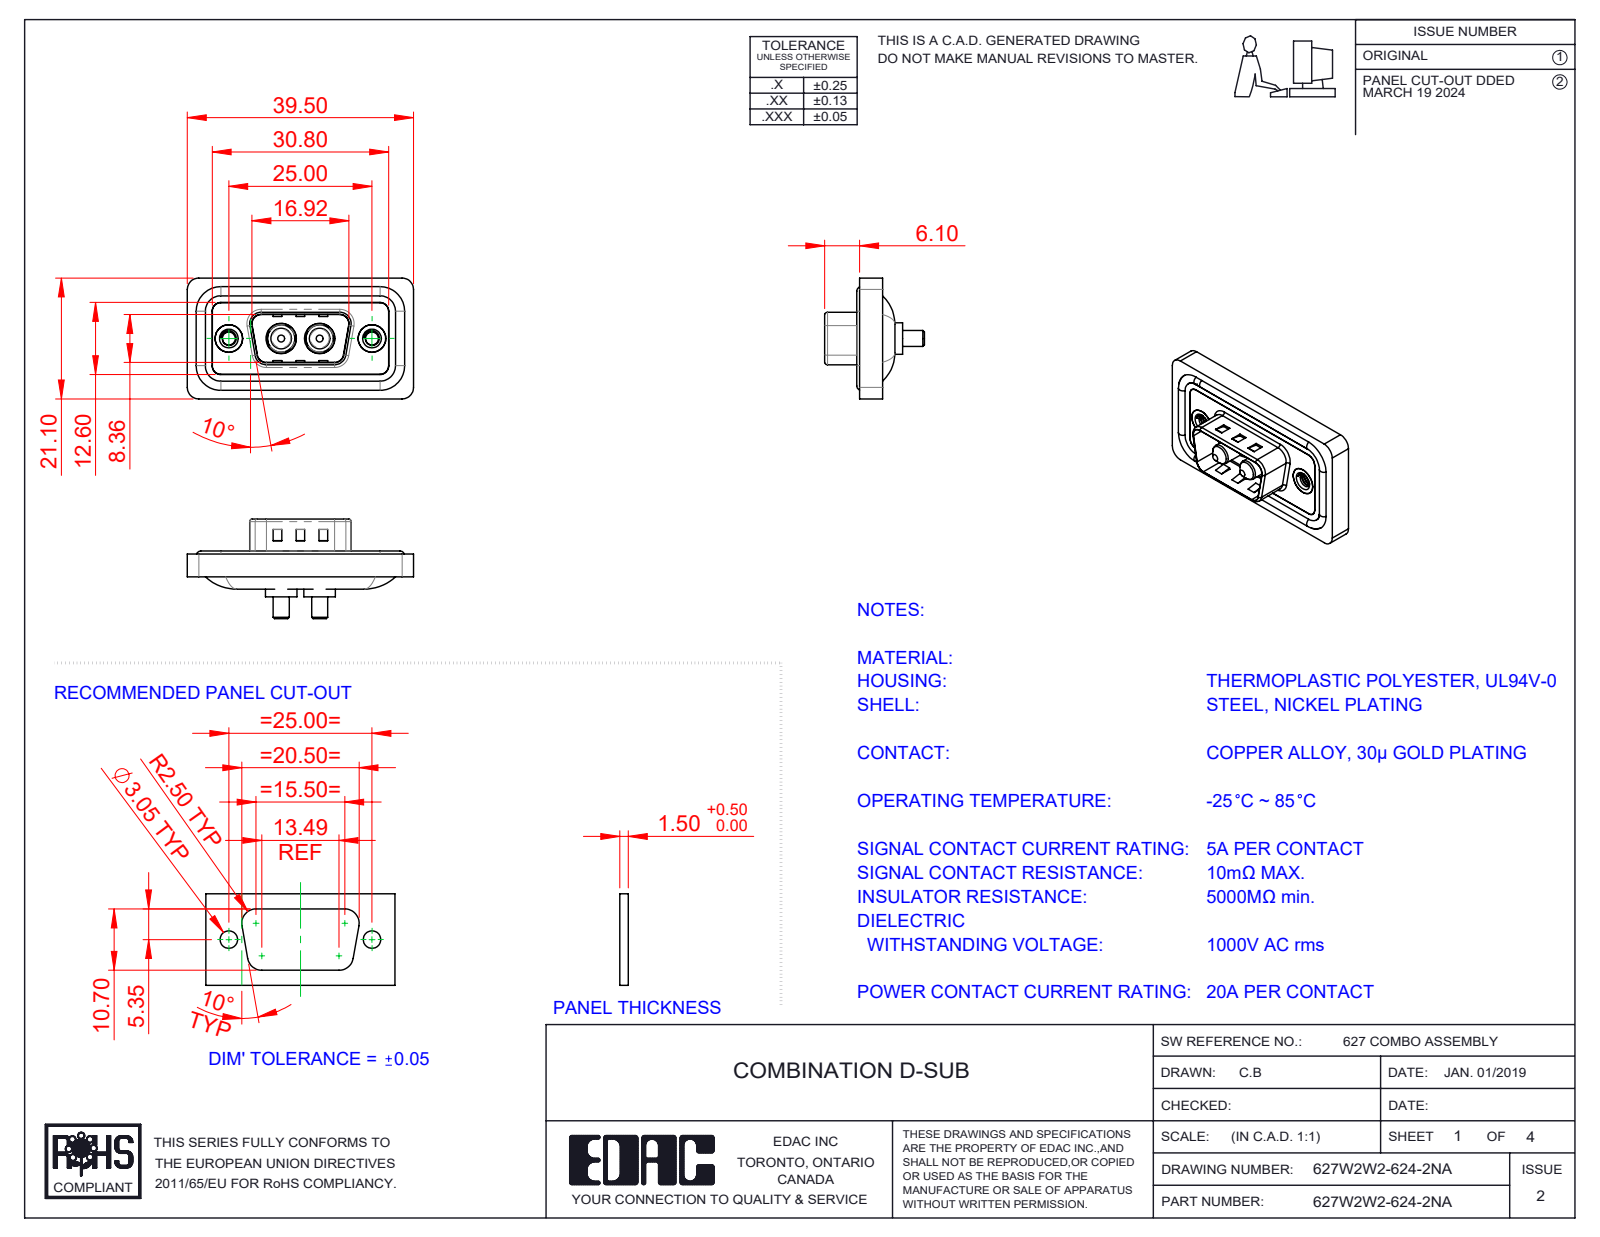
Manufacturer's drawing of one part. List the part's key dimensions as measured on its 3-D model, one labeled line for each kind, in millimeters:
Part name (STEP PRODUCT): 627W2W2-624-2NA; 627Combo Waterproof Housing_09 Contacts; 627Combo Shell Front_09 Contacts; 627Combo Shell Rear_09 Contacts (+3 more)
STEP written by: SolidWorks 2023 (CONFIG_CONTROL_DESIGN)
Units: millimetres
Bodies: 11 solids, 487 faces (165 planar, 220 cylindrical, 102 other)
Overall size (bounding box): 39.5 × 21.1 × 17.4
Volume: 4 462 mm³ · Surface area: 6 981 mm²
Round holes (diameter × count): ⌀2.26 ×2, ⌀4 ×2, ⌀4.8 ×2, ⌀4.85 ×2, ⌀5 ×2, ⌀5.3 ×2
Round bosses / shafts (diameter × count): ⌀1.6 ×4, ⌀5.5 ×2, ⌀5.2 ×2, ⌀4.9 ×2, ⌀4.75 ×2, ⌀3.75 ×2, ⌀3.6 ×2, ⌀2.8 ×2
Partial cylindrical surfaces — rounded edges, fillets, slot ends (radius × count): R1.5 ×22, R2 ×18, R0.5 ×8, R1.6 ×8, R0.25 ×4, R0.6 ×4, R0.65 ×4, R0.9 ×4
Main face-to-face distances: 0.4, 1.1, 2.9, 3.1, 0.5, 1.6, 1.5, 4, 2.5, 0.7
Hole centre spacings: 9.14, 15.86, 6.72, 25
